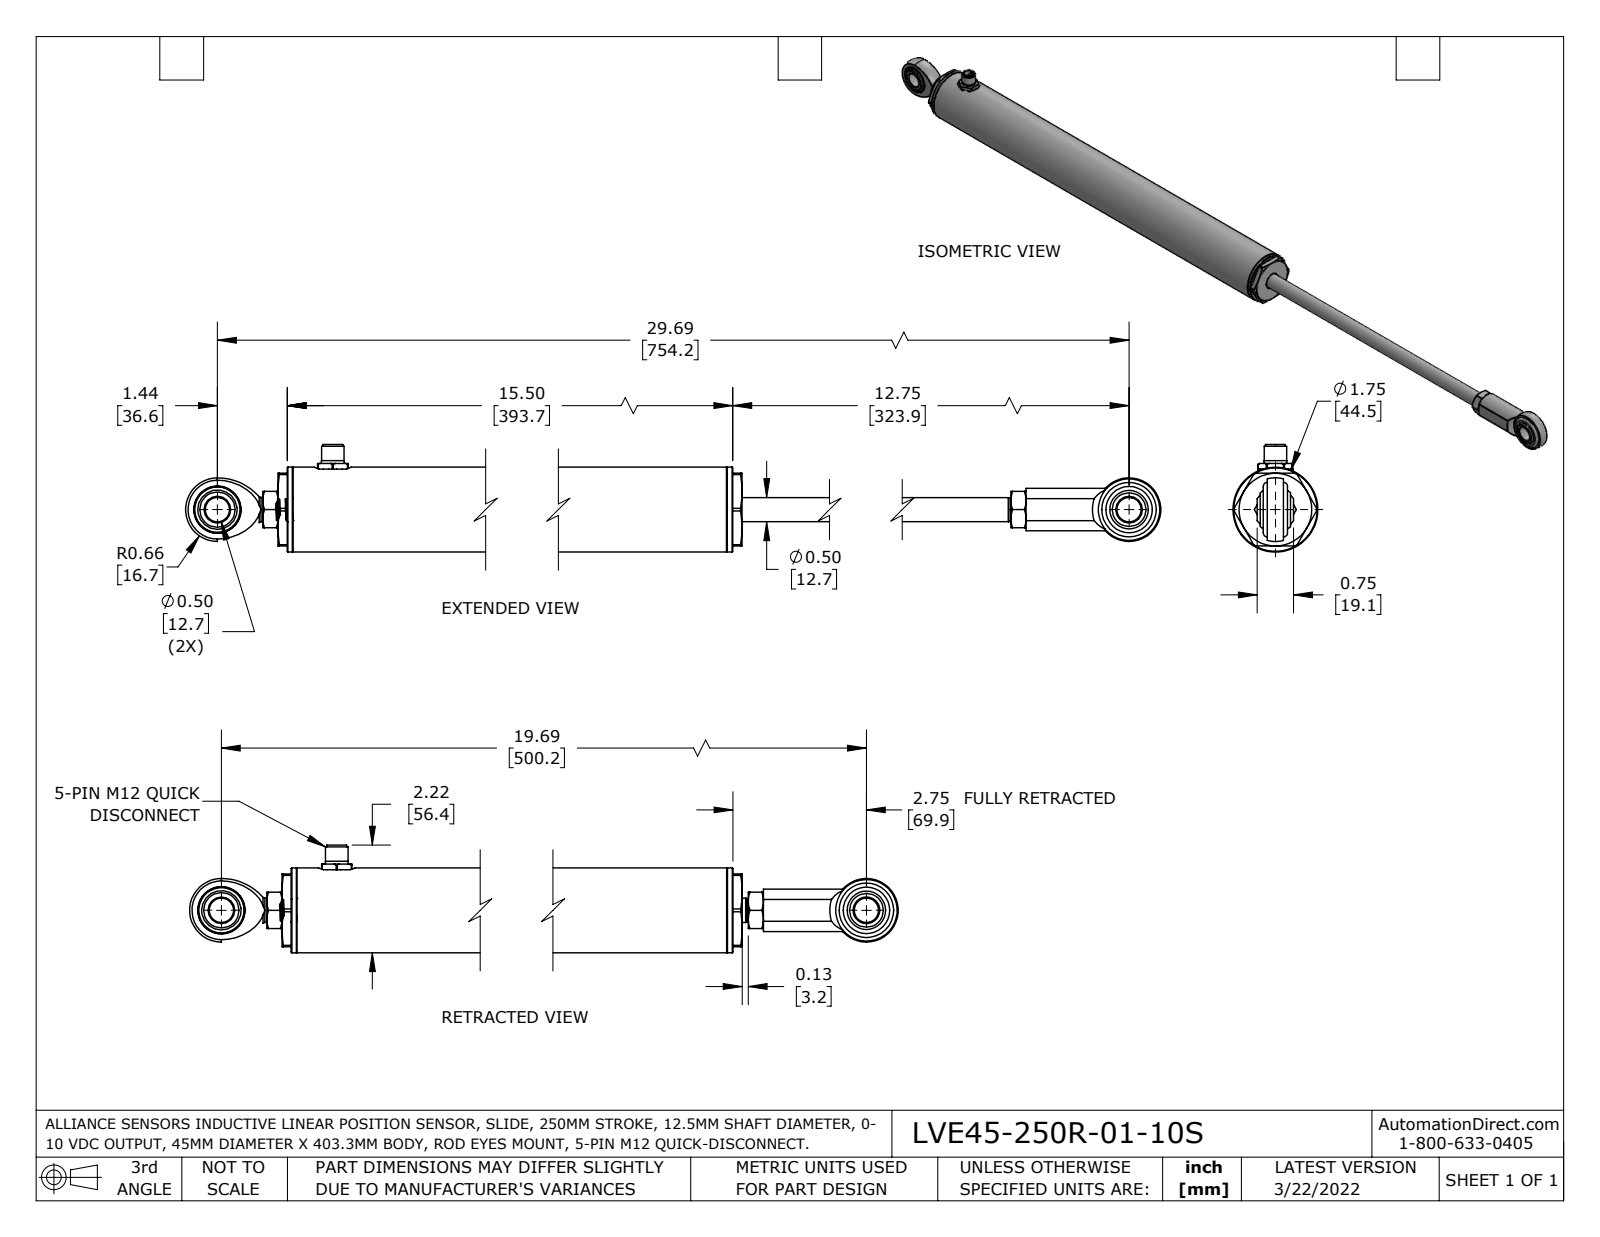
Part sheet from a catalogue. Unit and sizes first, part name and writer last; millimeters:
Units: millimetres
Overall size (bounding box): 787.5 × 56.4 × 44.5
Round holes (diameter × count): ⌀12.7 ×3, ⌀5 ×1, ⌀6.4 ×1, ⌀6.7 ×1, ⌀7.8 ×1, ⌀8.4 ×1, ⌀8.6 ×1, ⌀10.5 ×1, ⌀10.6 ×1, ⌀11.5 ×1, ⌀12.1 ×1, ⌀12.7 ×1
Round bosses / shafts (diameter × count): ⌀0.8 ×5, ⌀44.5 ×1, ⌀41.3 ×1, ⌀39.7 ×1, ⌀38.9 ×1, ⌀38.1 ×1, ⌀37.3 ×1, ⌀35.2 ×1
Partial cylindrical surfaces — rounded edges, fillets, slot ends (radius × count): R8.3 ×1, R9 ×1, R9.6 ×1, R9.7 ×1, R11.1 ×1, R21.6 ×1
Main face-to-face distances: 49, 12.7, 9.7, 17.5, 66.5, 344.8, 56.9, 39.4, 349.6, 332.1
Hole centre spacings: 12.7, 754.2
Volume: 310 200 mm³ · Surface area: 183 000 mm²
Bodies: 23 solids, 873 faces (198 planar, 297 cylindrical, 378 other)
Part name (STEP PRODUCT): 3100-0020; 5500-0013, PCB (Dia .685)_MHPE; 3100-0012-YY; 3100-0041-XX-Z_3100-0041-10-Z (+8 more)
STEP written by: SolidWorks 2021 (AUTOMOTIVE_DESIGN)
